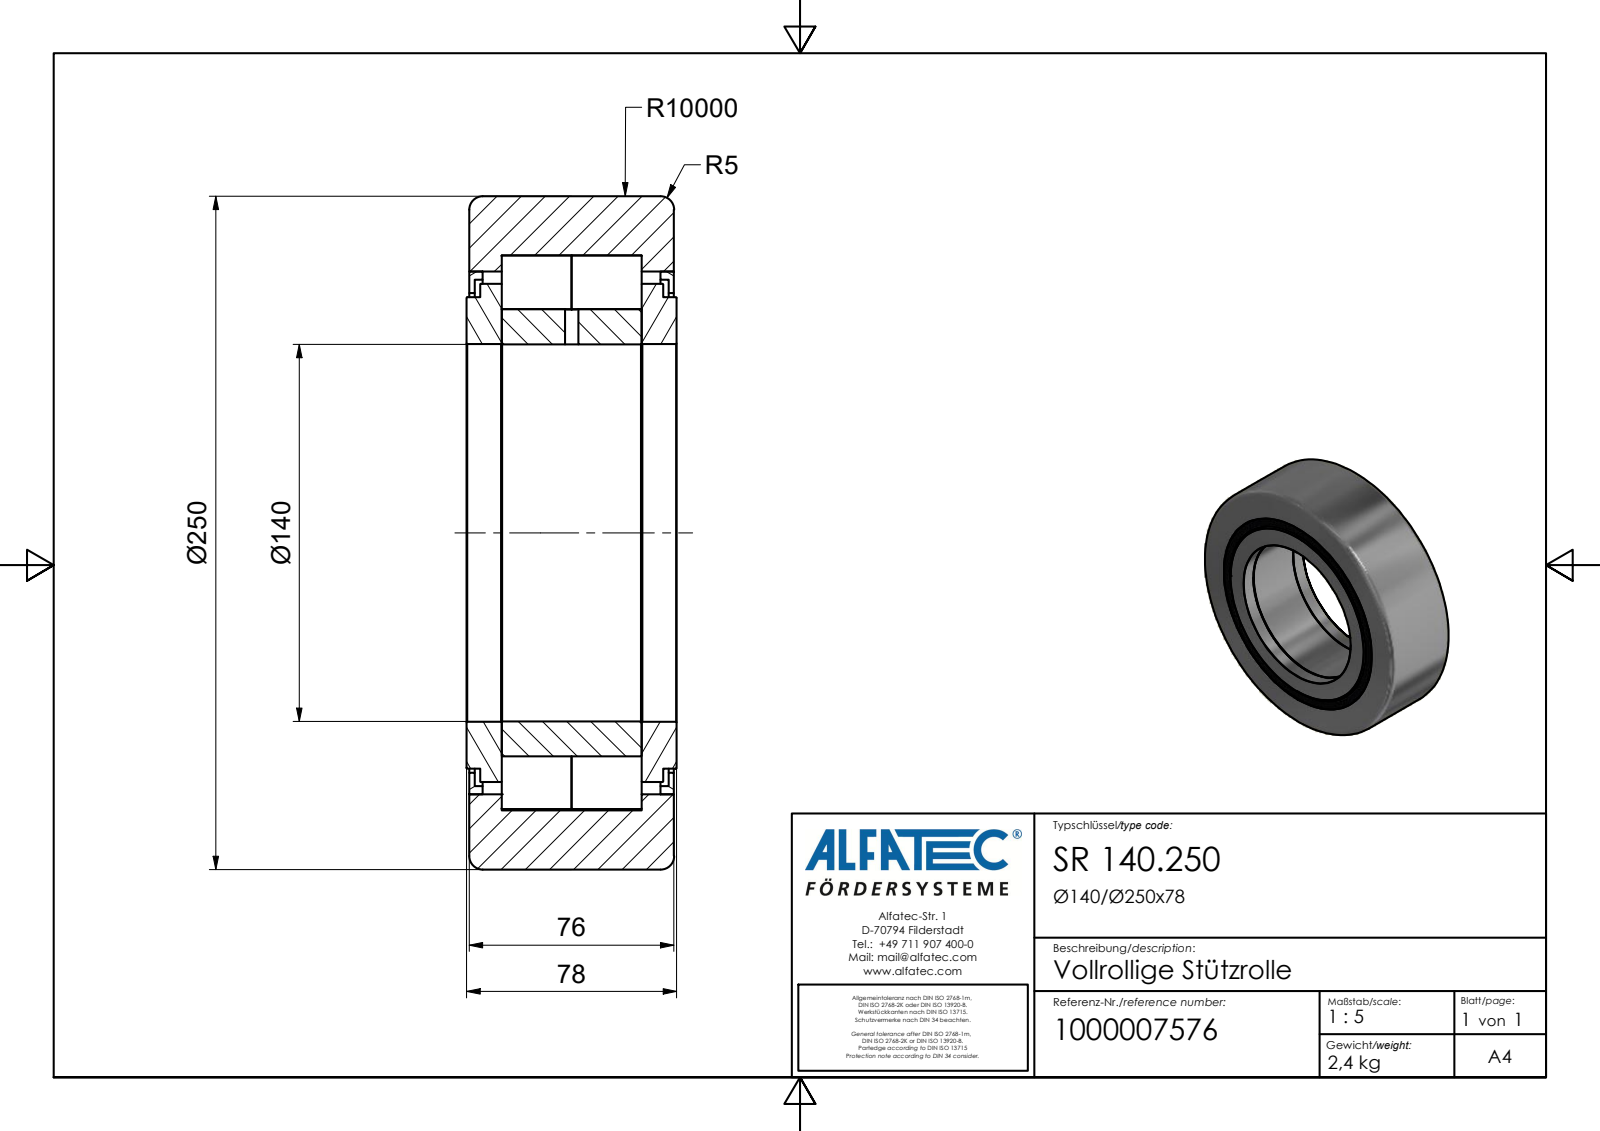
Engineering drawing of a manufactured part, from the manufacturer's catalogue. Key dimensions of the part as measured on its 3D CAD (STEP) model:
Part name (STEP PRODUCT): SR 140.250_Kontur
STEP written by: Autodesk Inventor 2020 (AUTOMOTIVE_DESIGN)
Units: millimetres
Bodies: 2 solids, 51 faces (18 planar, 16 cylindrical, 17 other)
Overall size (bounding box): 250 × 250 × 78
Volume: 1 901 000 mm³ · Surface area: 279 264 mm²
Round holes (diameter × count): ⌀5 ×1, ⌀140 ×1, ⌀140.3 ×1, ⌀178 ×1, ⌀188 ×1, ⌀194 ×1, ⌀206 ×1
Round bosses / shafts (diameter × count): ⌀185 ×1, ⌀175 ×1, ⌀166 ×1
Main face-to-face distances: 1, 76, 12, 64, 13, 65, 77, 72, 2, 3
